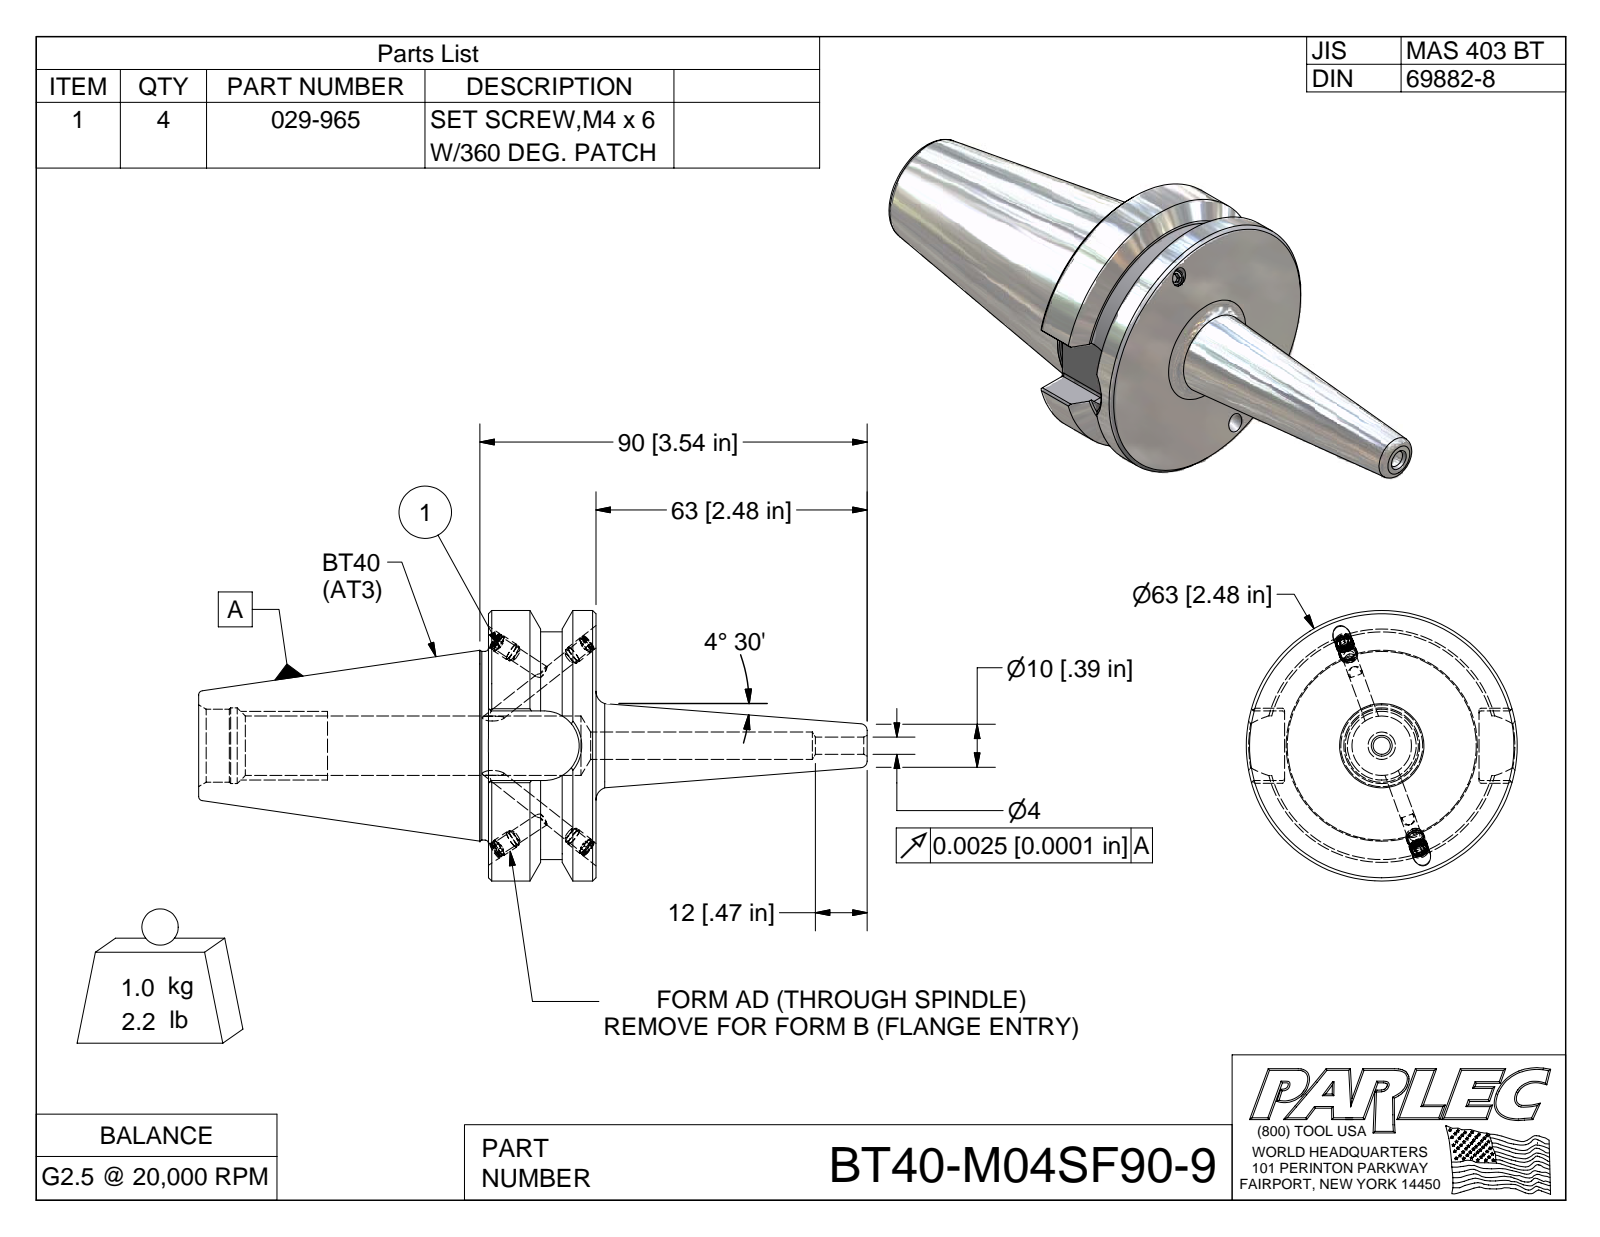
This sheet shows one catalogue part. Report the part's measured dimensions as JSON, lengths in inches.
{"part_name": "BT40-M04SF90-9; BT40BC-M04SF90-9-1; 029-965", "step_written_by": "Autodesk Inventor 2009 (AUTOMOTIVE_DESIGN)", "units": "inches", "bodies": {"solids": 5, "faces": 149, "planar": 67, "cylindrical": 39, "other": 43}, "overall_size": [6.118, 2.48, 2.48], "volume_in3": 7.866, "surface_area_in2": 42.78, "round_holes": [[0.13, 4], [0.161, 4], [0.157, 1], [0.694, 1]], "round_bosses_or_shafts": [[0.165, 4], [0.157, 4], [2.48, 1], [2.087, 1], [1.75, 1], [1.73, 1]], "partial_cylinders_radius": [[0.02, 8], [0.319, 1]], "face_to_face_distances": [0.984, 1.78, 2.653, 3.637, 0.637, 3.328, 0.675, 0.309, 3.131, 0.478]}
